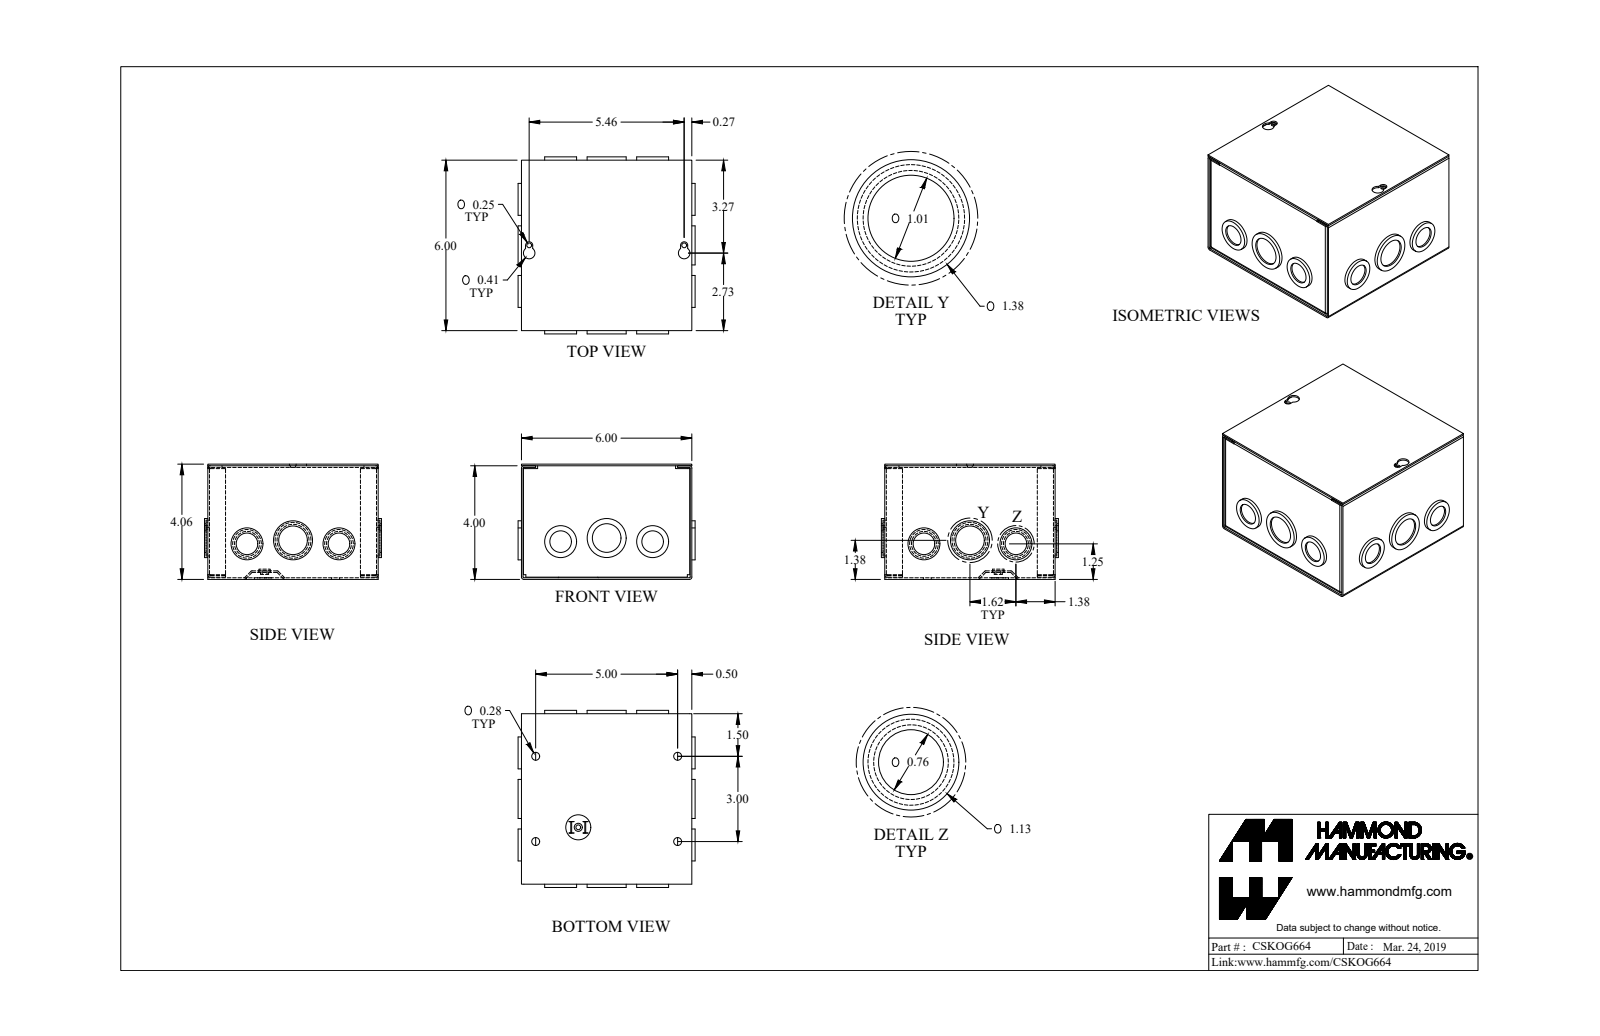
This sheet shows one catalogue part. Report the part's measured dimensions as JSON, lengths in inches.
{"part_name": "CSKOG664_Default", "step_written_by": "SolidWorks 2019 (CONFIG_CONTROL_DESIGN)", "units": "inches", "bodies": {"solids": 4, "faces": 333, "planar": 169, "cylindrical": 156, "other": 8}, "overall_size": [6.234, 6.234, 4.057], "volume_in3": 11.12, "surface_area_in2": 397, "round_holes": [[1.011, 6], [0.281, 4], [0.761, 4], [0.17, 3], [1.261, 2], [0.5, 1]], "round_bosses_or_shafts": [[1.125, 5], [0.875, 4], [0.875, 3], [1.375, 2], [1.125, 1], [0.492, 1], [0.284, 1]], "partial_cylinders_radius": [[0.029, 12], [0.086, 12], [0.057, 8], [0.125, 2], [0.203, 2]], "face_to_face_distances": [0.057, 5.943, 4, 6, 3.943, 5.886, 4.057, 0.07, 5.873, 0.114], "hole_center_spacings": [1.517, 1.625, 5.441, 3, 3.24, 5, 5.831, 1.5]}
